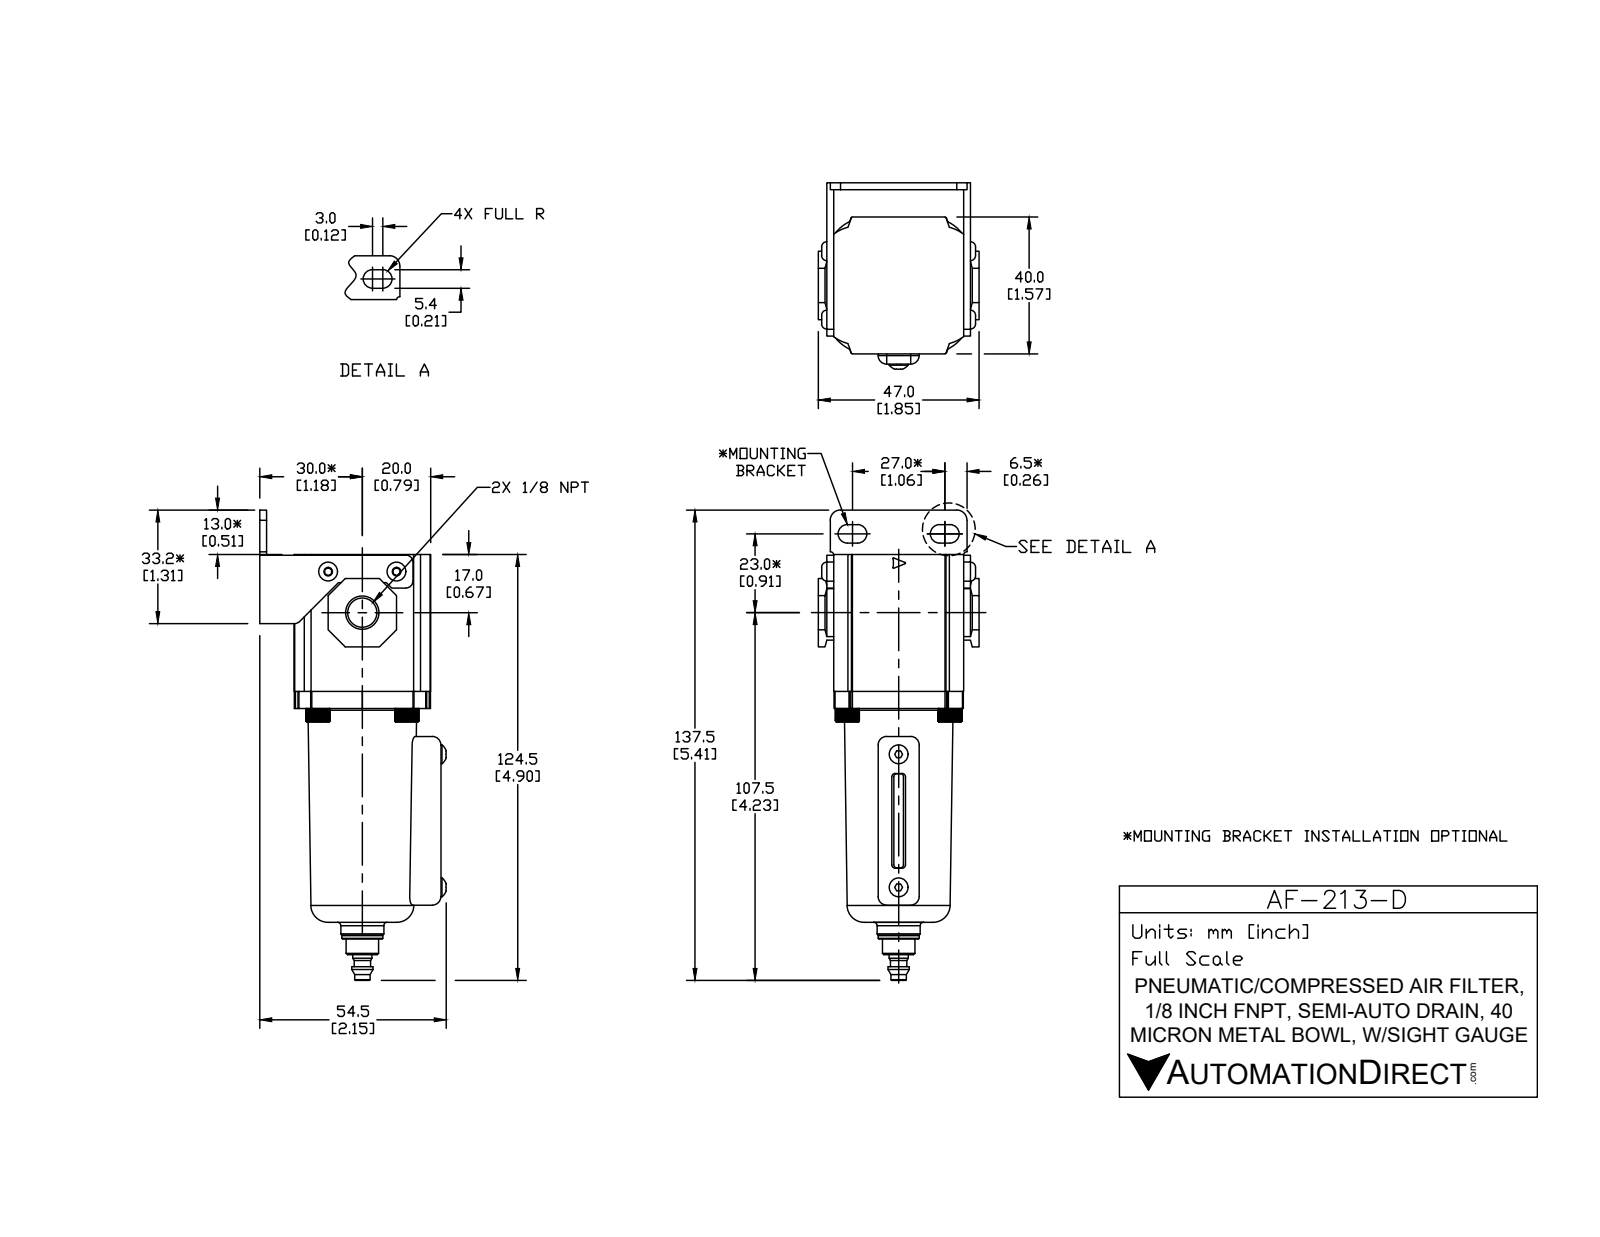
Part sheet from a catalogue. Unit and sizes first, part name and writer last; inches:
Units: inches
Overall size (bounding box): 5.413 × 2.165 × 1.85
Round holes (diameter × count): ⌀0.134 ×2, ⌀0.118 ×1, ⌀0.332 ×1
Round bosses / shafts (diameter × count): ⌀0.276 ×4, ⌀0.217 ×2, ⌀0.496 ×1, ⌀0.472 ×1, ⌀0.375 ×1, ⌀0.374 ×1, ⌀0.244 ×1, ⌀0.22 ×1
Partial cylindrical surfaces — rounded edges, fillets, slot ends (radius × count): R0.012 ×12, R0.051 ×8, R0.098 ×8, R0.079 ×5, R0.02 ×4, R0.039 ×4, R0.106 ×4, R0.469 ×4
Main face-to-face distances: 1.575, 0.079, 1.496, 0.315, 0.394, 1.969, 1.89, 0.512, 0.591, 1.654
Hole centre spacings: 0.615, 0.787
Volume: 7.412 in³ · Surface area: 47.1 in²
Bodies: 9 solids, 385 faces (216 planar, 107 cylindrical, 62 other)
Part name (STEP PRODUCT): AF-213-D
STEP written by: SolidWorks 2015 (CONFIG_CONTROL_DESIGN)
